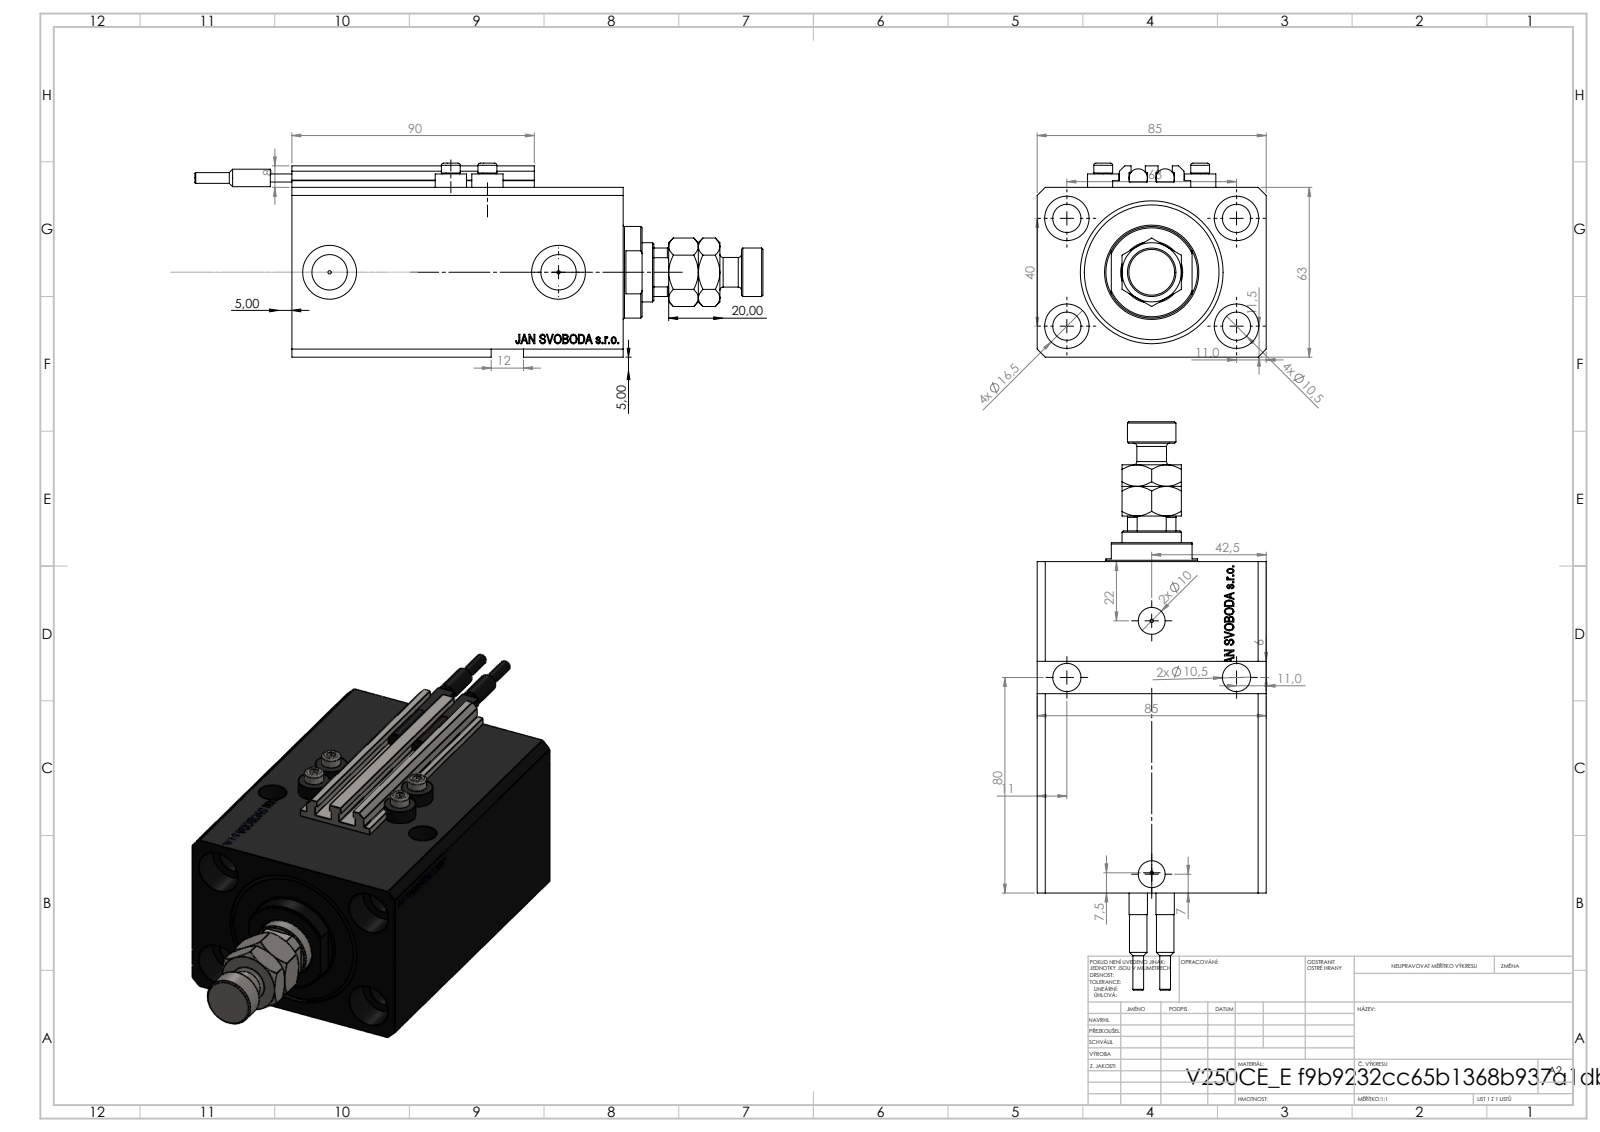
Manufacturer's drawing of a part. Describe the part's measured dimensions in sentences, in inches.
The part is named "V250CE_VC_E; MFA; SWITCH_V250CE; V250CE_E_Body (+2 more)". Its 3-D file was written by "SolidWorks 2019 (CONFIG_CONTROL_DESIGN)". It is 11 solids with 1211 faces: 583 planar, 162 cylindrical and 466 other. Overall it measures 8.307 by 3.346 by 2.835 inches. Its volume is 34.84 cubic inches and its surface area 194.2 square inches. Round holes: 8 of diameter 0.413, 4 of diameter 0.049, 4 of diameter 0.157, 4 of diameter 0.65, 2 of diameter 0.394, 2 of diameter 0.518, 2 of diameter 0.787, 1 of diameter 0.492, 1 of diameter 0.866, 1 of diameter 1.575, 1 of diameter 2.087. Round bosses or shafts: 4 of diameter 0.457, 4 of diameter 0.276, 2 of diameter 0.268, 2 of diameter 0.256, 2 of diameter 0.157, 1 of diameter 1.339, 1 of diameter 0.709, 1 of diameter 0.433. Partial cylindrical surfaces (rounded edges, fillets, slot ends): 10 of radius 0.008, 1 of radius 0.413. The main face-to-face distances are 2.48, 3.346, 0.669, 4.843, 4.173, 0.118, 0.449, 3.724, 4.394, 2.559. The hole center spacings are 1.469, 2.48, 0.535, 0.606, 0.983, 1.084, 1.324, 1.417.
